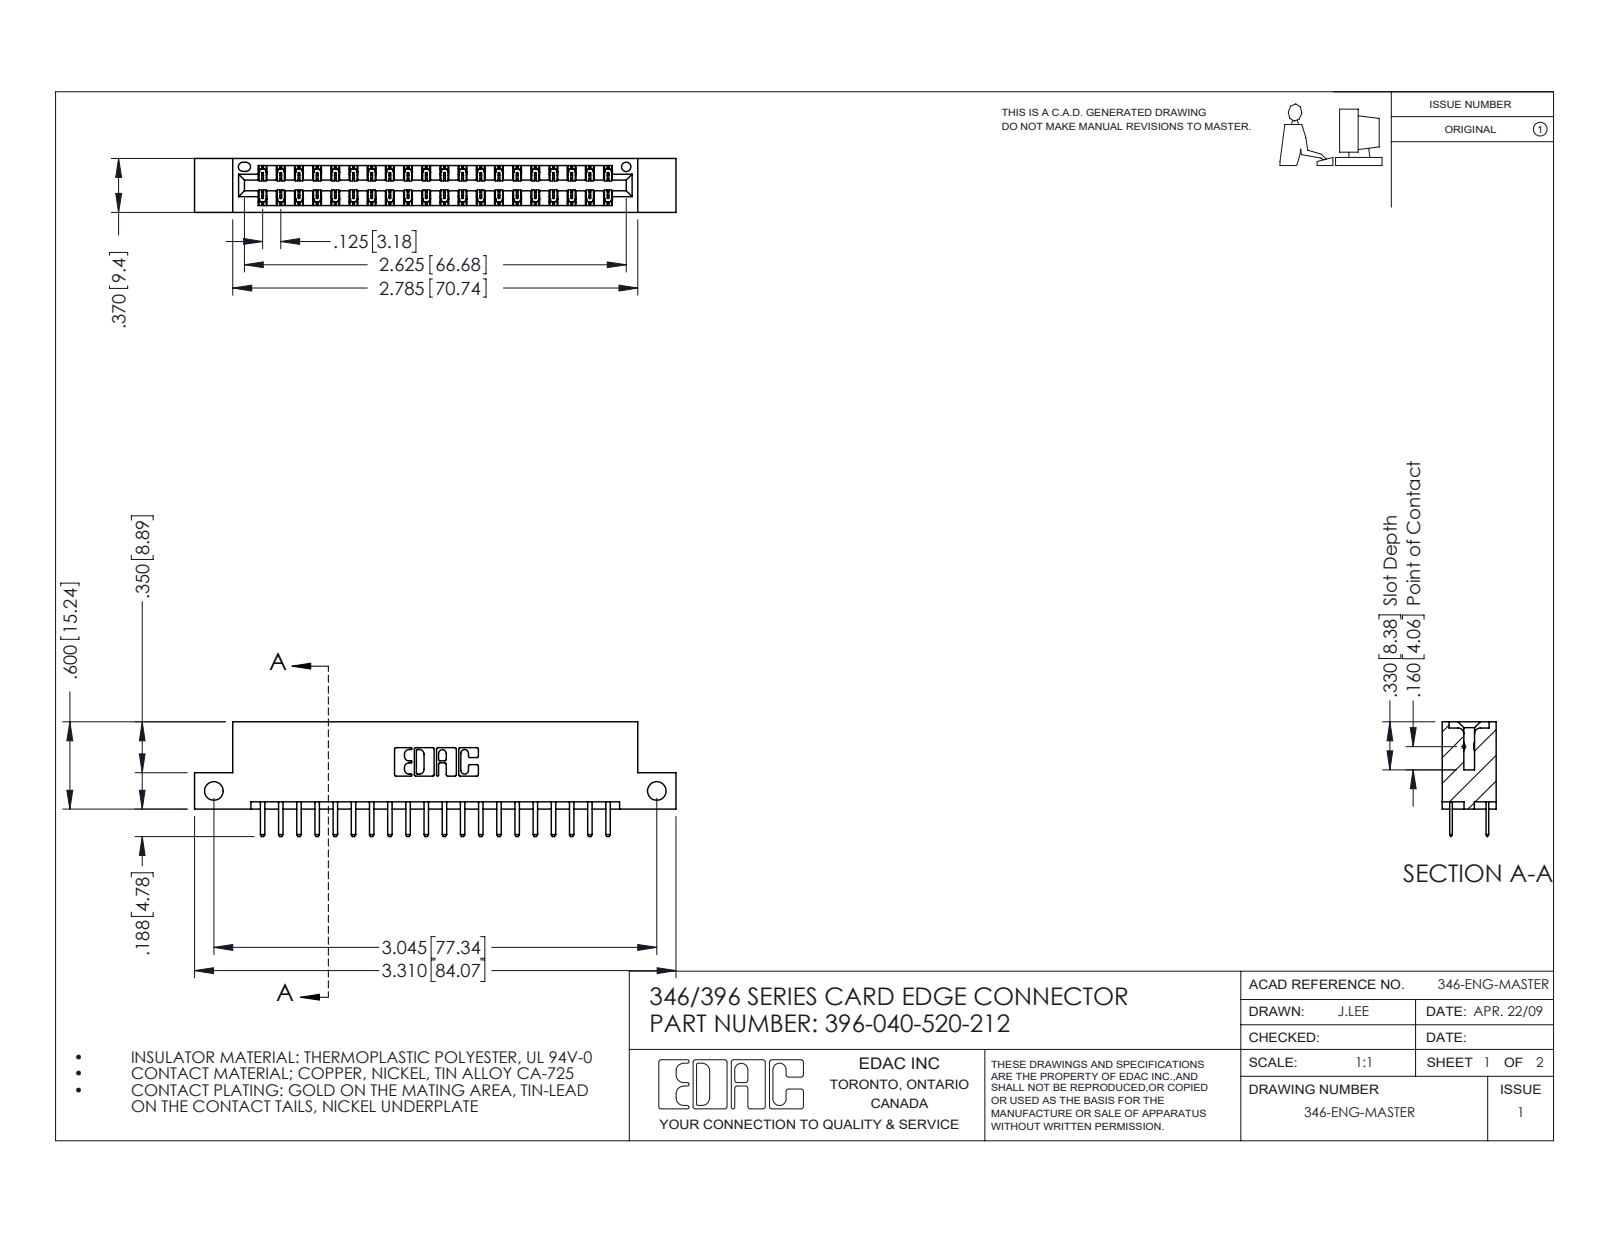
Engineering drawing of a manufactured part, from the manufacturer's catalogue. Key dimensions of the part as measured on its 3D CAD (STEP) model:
Part name (STEP PRODUCT): 345-292-001_345-293-120; 346 Part_Flush Mounting Lugs - Side Mount; 396-040-520-212
STEP written by: SolidWorks 2016 (CONFIG_CONTROL_DESIGN)
Units: inches
Bodies: 41 solids, 2362 faces (1556 planar, 806 cylindrical, 0 other)
Overall size (bounding box): 3.31 × 0.788 × 0.37
Volume: 0.483 in³ · Surface area: 16.07 in²
Round holes (diameter × count): ⌀0.128 ×2, ⌀0.064 ×1
Partial cylindrical surfaces — rounded edges, fillets, slot ends (radius × count): R0.006 ×60, R0.01 ×44, R0.01 ×22, R0.007 ×6, R0.031 ×6, R0.026 ×3, R0.014 ×2, R0.022 ×2
Main face-to-face distances: 0.048, 0.322, 0.25, 0.37, 0.275, 0.072, 0.298, 0.025, 0.148, 0.222
Hole centre spacings: 3.045
